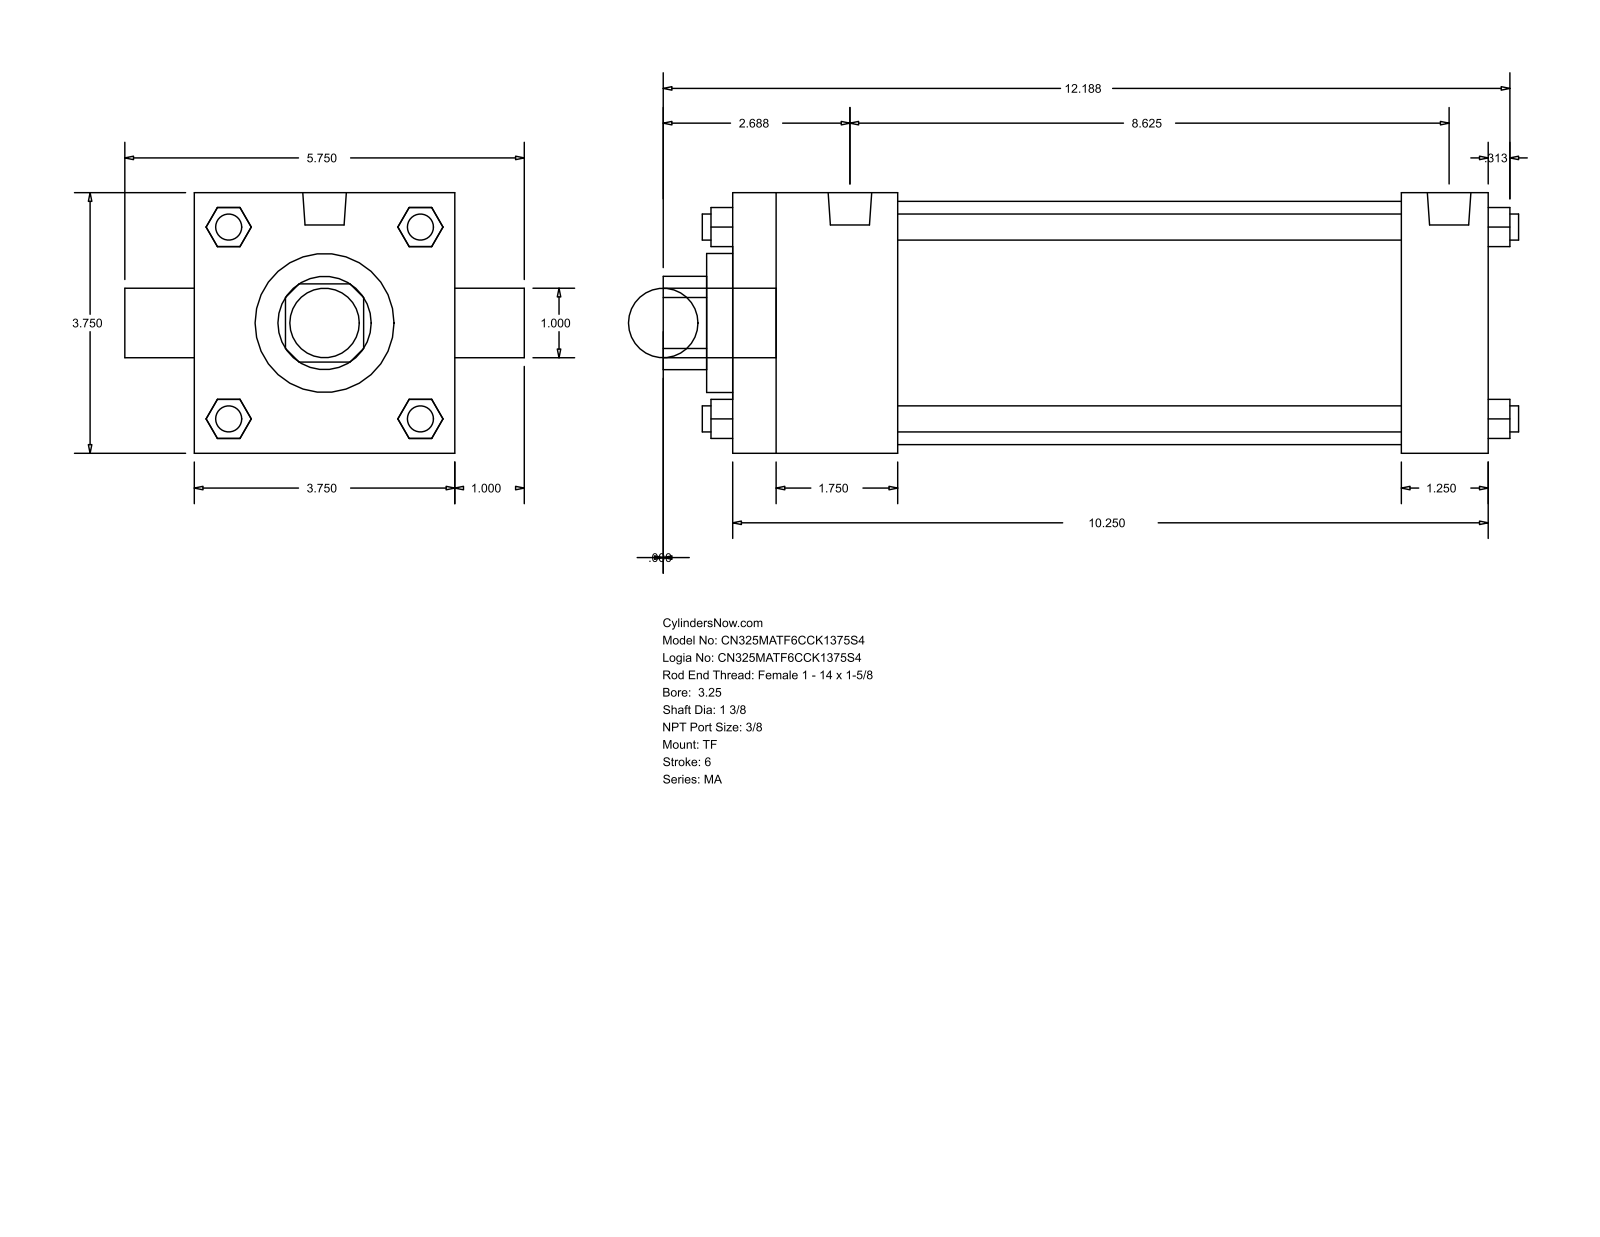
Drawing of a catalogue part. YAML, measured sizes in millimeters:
part_name: "MA_TF__0325_1.375"
step_written_by: "GSSL Pune (CONFIG_CONTROL_DESIGN)"
units: millimeters
bodies: {solids: 0, faces: 120, planar: 92, cylindrical: 28, other: 0}
overall_size: [312.74, 146.05, 95.25]
round_holes:
  - {diameter: 25.4, count: 1}
  - {diameter: 34.92, count: 1}
  - {diameter: 50.8, count: 1}
  - {diameter: 88.9, count: 1}
round_bosses_or_shafts:
  - {diameter: 9.53, count: 4}
  - {diameter: 11.11, count: 3}
  - {diameter: 15.93, count: 2}
  - {diameter: 25.4, count: 1}
partial_cylinders:
  - {radius: 17.06, count: 1}
face_to_face_distances: [95.24, 276.22, 60.32, 244.48, 184.16, 215.9, 31.74, 9.52, 69.84, 254]
